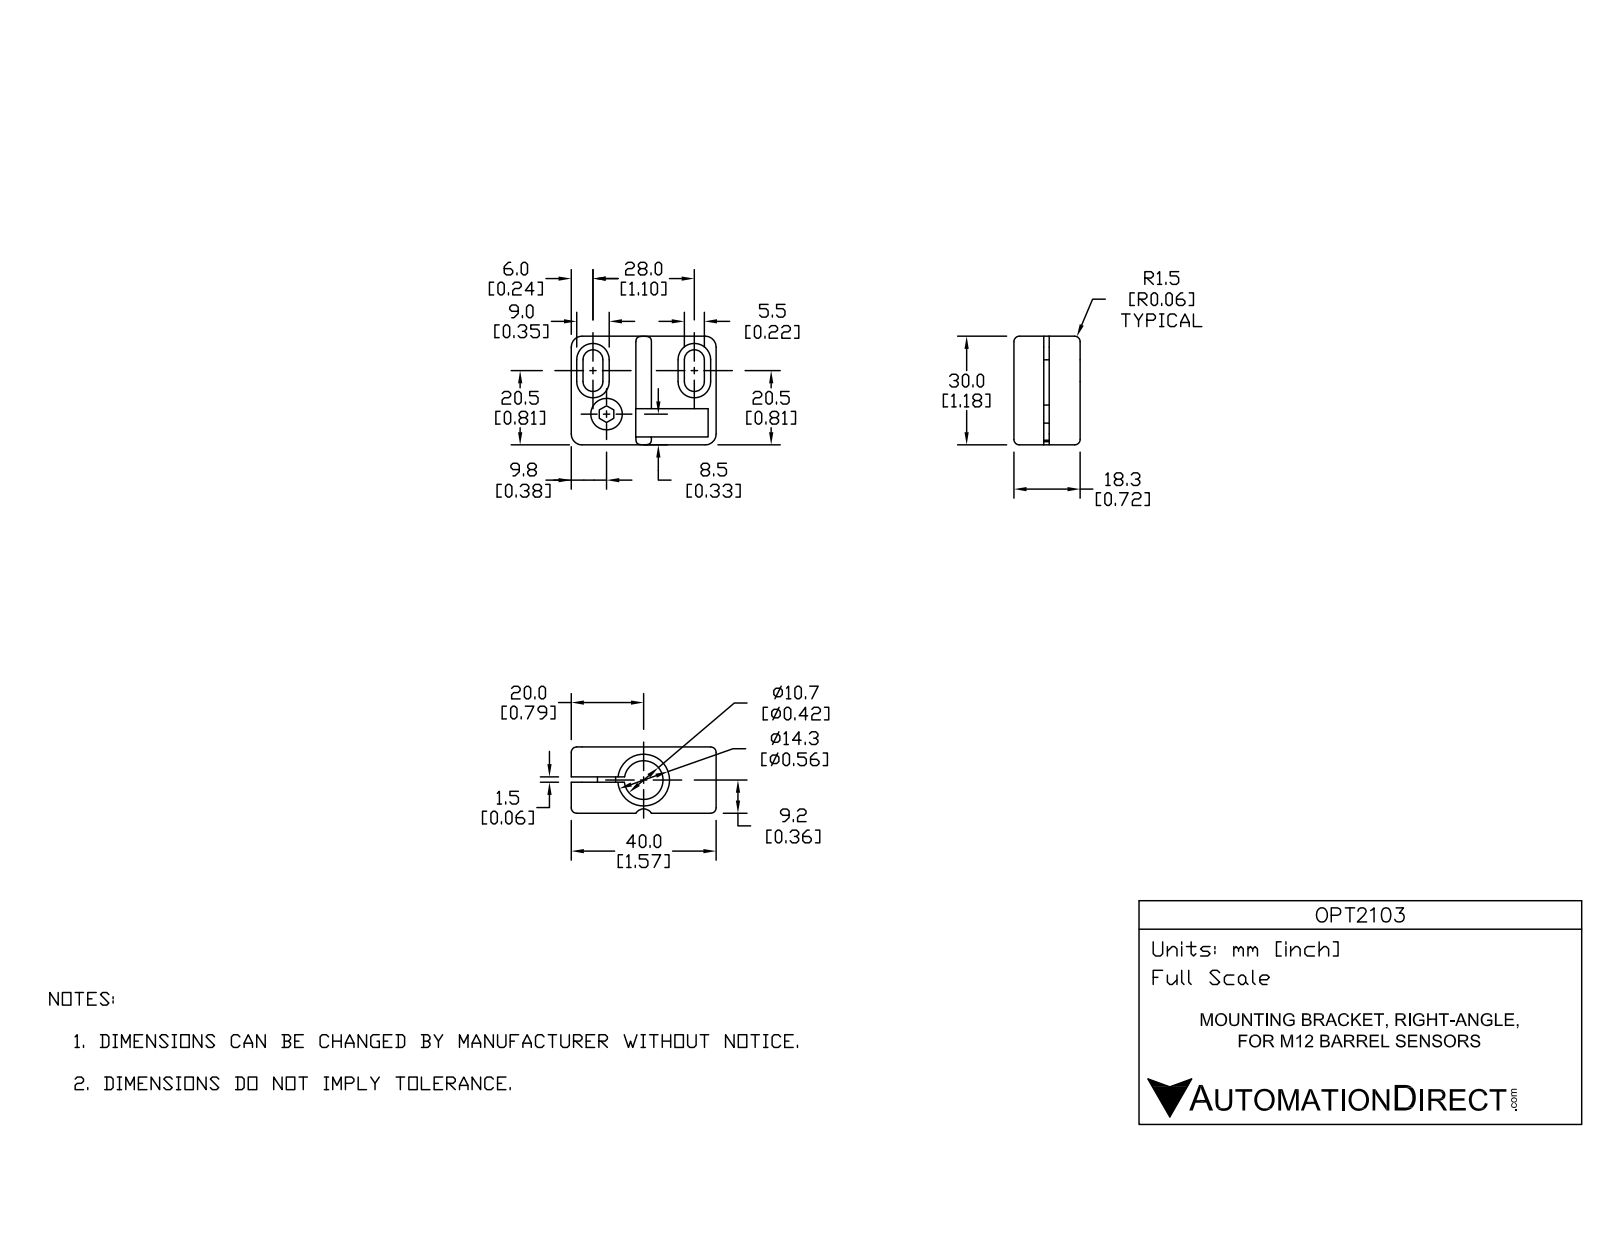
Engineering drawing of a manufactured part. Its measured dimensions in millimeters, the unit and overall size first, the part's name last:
Units: millimetres
Overall size (bounding box): 40 × 30 × 18.3
Round holes (diameter × count): ⌀5.5 ×1, ⌀8.7 ×1, ⌀12 ×1
Round bosses / shafts (diameter × count): ⌀8.5 ×1, ⌀5 ×1
Partial cylindrical surfaces — rounded edges, fillets, slot ends (radius × count): R1.5 ×8, R2.75 ×4, R3 ×4, R4.5 ×4, R2.5 ×1
Main face-to-face distances: 1.5, 8.55, 18.3, 8.25, 30, 10.05, 9.75, 40, 1.75, 7.25
Volume: 14 024 mm³ · Surface area: 7 519 mm²
Bodies: 1 solid, 73 faces (34 planar, 29 cylindrical, 10 other)
Part name (STEP PRODUCT): 56 10 30 12
STEP written by: Unknown (AUTOMOTIVE_DESIGN)
